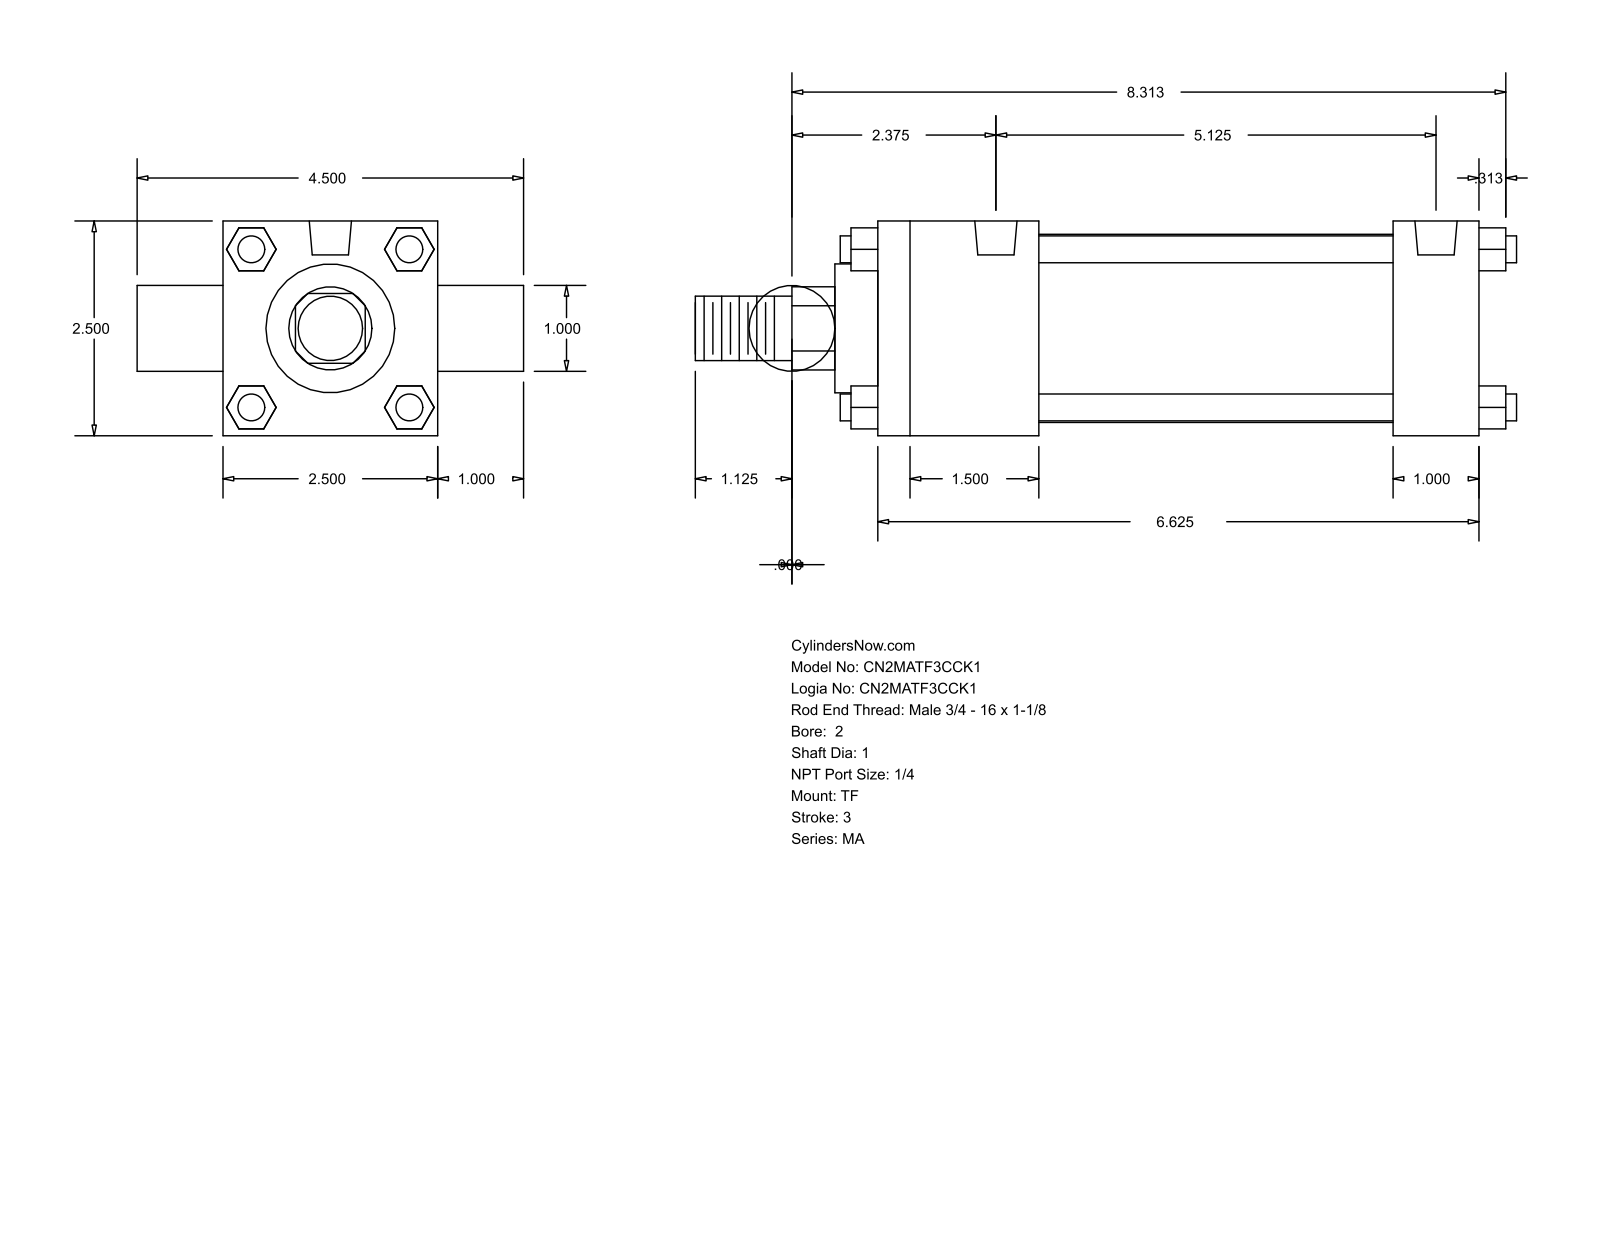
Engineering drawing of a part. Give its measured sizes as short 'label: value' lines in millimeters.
name: MA_TF__0200_1
written by: GSSL Pune (CONFIG_CONTROL_DESIGN)
unit: mm
bodies: 0 solids, 120 faces (92 planar, 28 cylindrical, 0 other)
size: 242.89 × 114.3 × 63.5
holes: 3× ⌀7.94, 2× ⌀12.49
bosses: 4× ⌀7.94, 2× ⌀25.4, 1× ⌀55.63, 1× ⌀38.1, 1× ⌀19.05
rounds: 1× R12.29
face distances: 63.5, 25.4, 177.8, 12.7, 47.63, 152.4, 104.77, 130.17, 88.9, 40.47
hole spacings: 130.17
